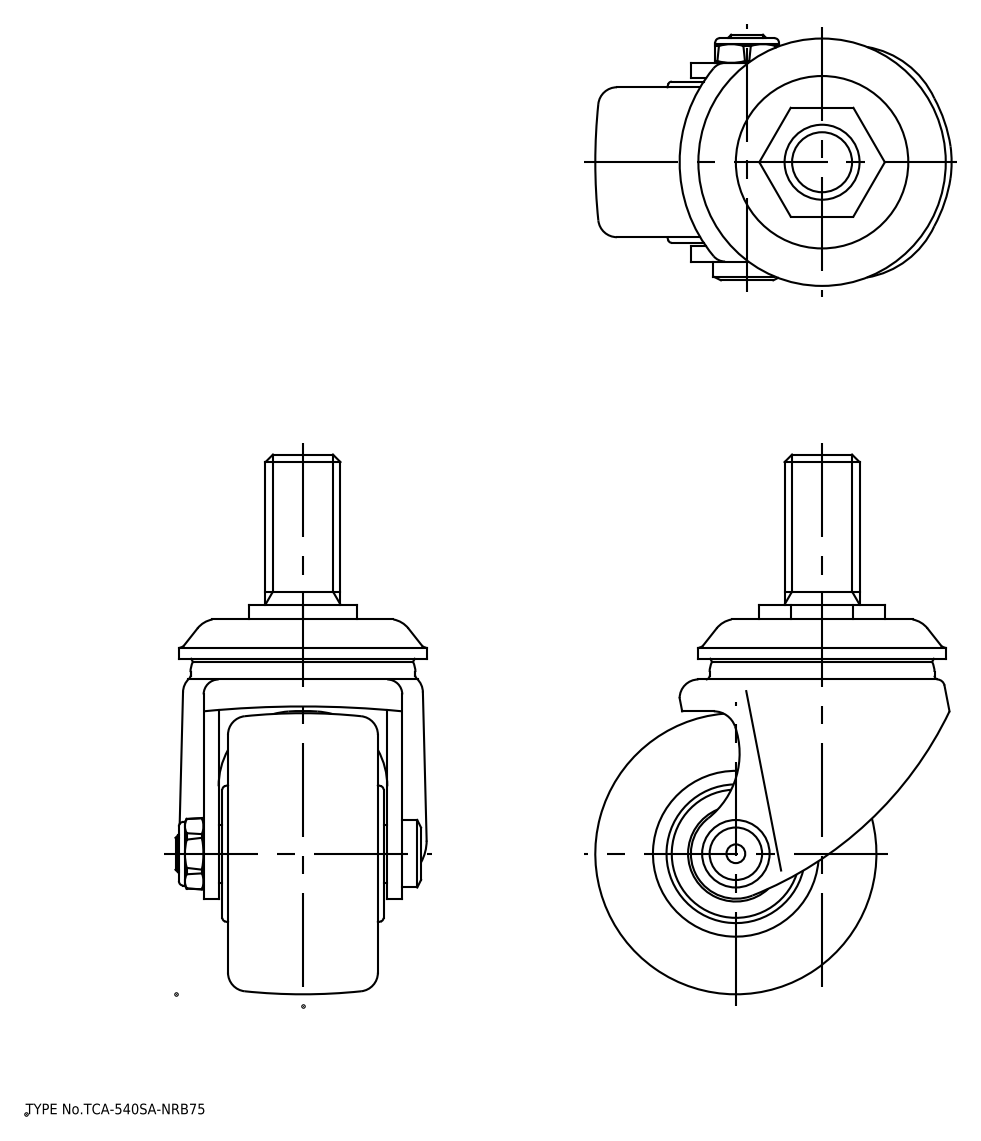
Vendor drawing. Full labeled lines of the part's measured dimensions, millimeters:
Part name (STEP PRODUCT): wheel
STEP written by: spGate 19.8.4 (****-****-****-****) (AUTOMOTIVE_DESIGN)
Units: millimetres
Bodies: 2 solids, 167 faces (42 planar, 47 cylindrical, 78 other)
Overall size (bounding box): 144 × 94.47 × 69.5
Volume: 275 950 mm³ · Surface area: 47 926 mm²
Round holes (diameter × count): ⌀1.15 ×2, ⌀10.2 ×1, ⌀33.1 ×1, ⌀54 ×1
Round bosses / shafts (diameter × count): ⌀66 ×1, ⌀60 ×1, ⌀33 ×1, ⌀20 ×1, ⌀18 ×1, ⌀17 ×1, ⌀15.6 ×1, ⌀10 ×1
Partial cylindrical surfaces — rounded edges, fillets, slot ends (radius × count): R5 ×3, R1 ×1, R2 ×1, R6 ×1, R12 ×1, R22 ×1, R31.71 ×1, R99 ×1
Main face-to-face distances: 4, 1.5, 41.5, 44, 1, 42.5, 2.5, 5, 20, 48
Hole centre spacings: 13.5, 27
